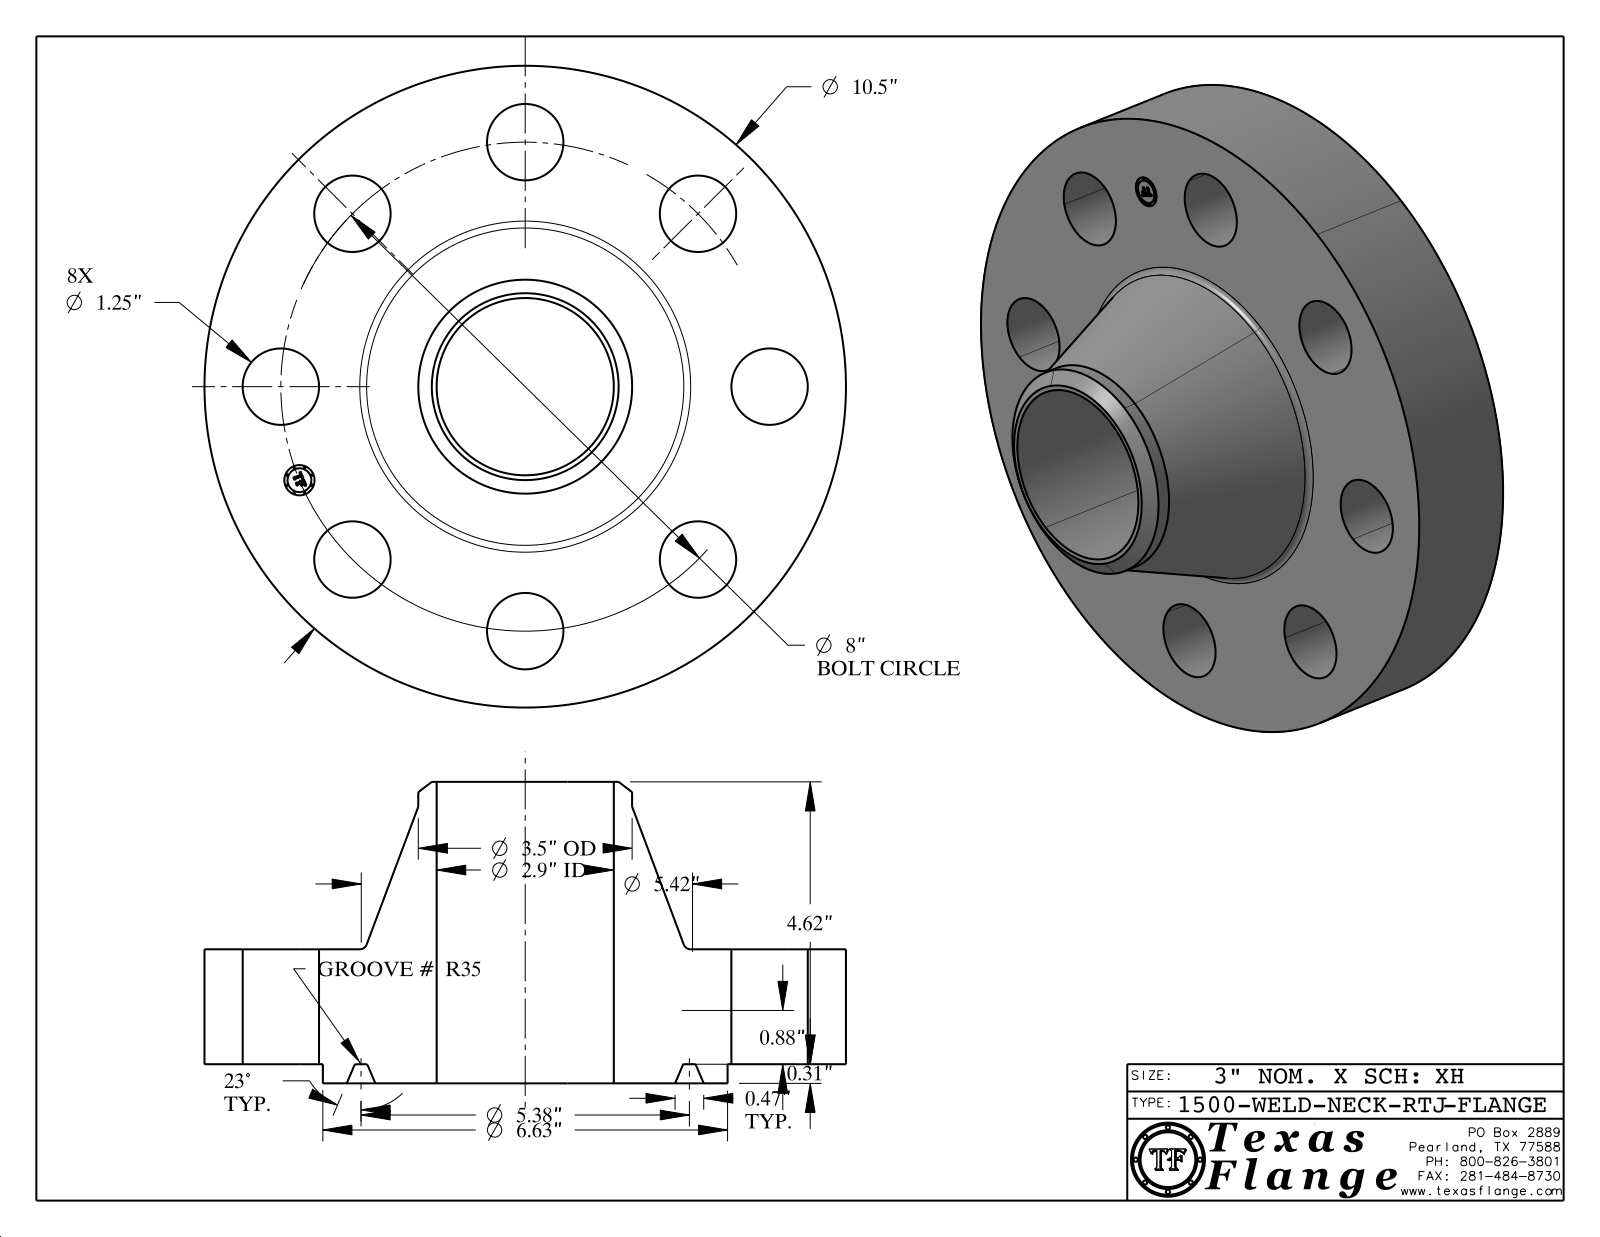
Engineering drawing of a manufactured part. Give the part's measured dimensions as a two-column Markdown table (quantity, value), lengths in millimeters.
| quantity | value |
| --- | --- |
| part name | 1500-WELD-NECK-RTJ |
| STEP written by | CATIA V5 STEP AP214 (AUTOMOTIVE_DESIGN) |
| units | millimeters |
| bodies | 1 solid, 429 faces (371 planar, 44 cylindrical, 14 other) |
| overall size | 266.7 × 266.7 × 125.3 |
| volume | 2 622 000 mm³ |
| surface area | 222 500 mm² |
| round holes (diameter × count) | 31.8 × 8, 12.6 × 1, 73.7 × 1 |
| round bosses / shafts (diameter × count) | 0.8 × 8, 266.7 × 1, 168.3 × 1, 88.9 × 1, 9.9 × 1 |
| main face-to-face distances | 47.8, 8, 55.7, 125.3, 117.3, 69.6, 0.4, 55.3, 47.4, 70 |
| hole center spacings | 101.6, 77.7, 143.7, 187.7, 39.6, 169, 199.3, 203.2 |
